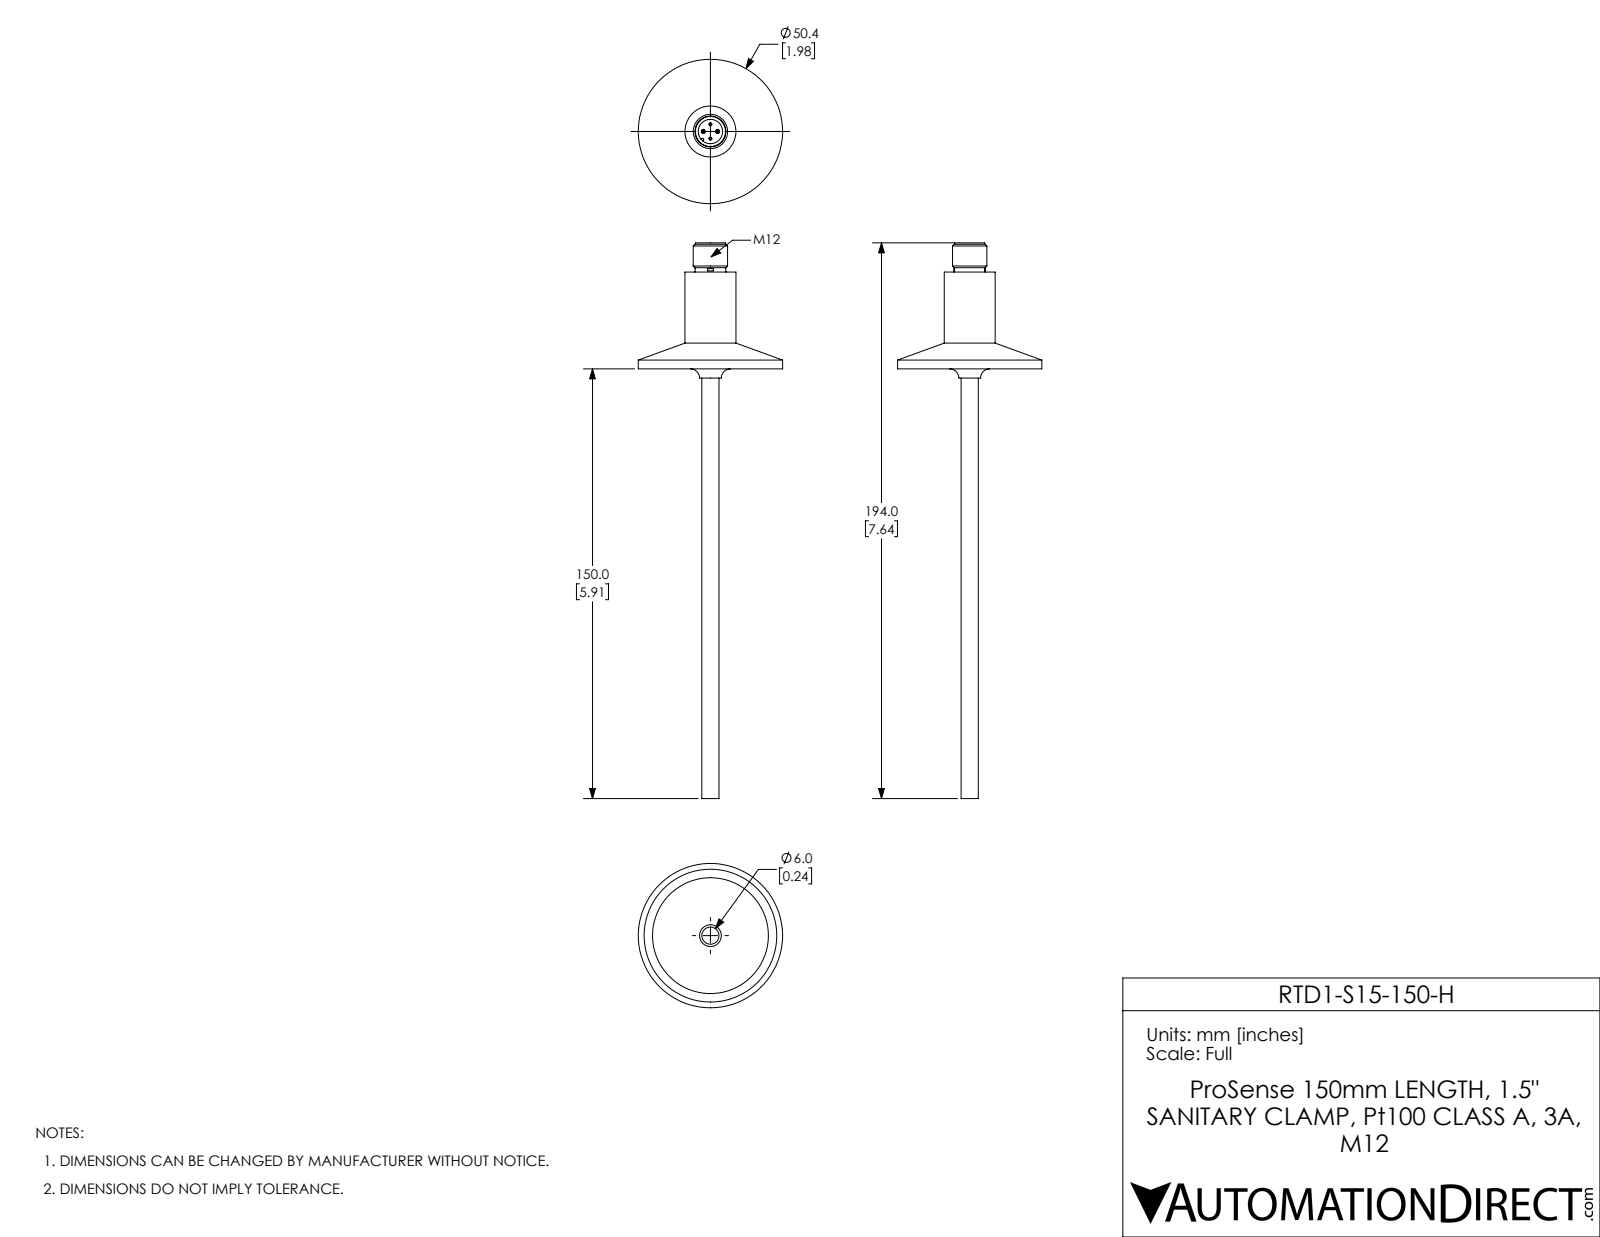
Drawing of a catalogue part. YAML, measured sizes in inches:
part_name: "RTD1-S15-150-H"
step_written_by: "SolidWorks 2017 (AUTOMOTIVE_DESIGN)"
units: inches
bodies: {solids: 1, faces: 79, planar: 26, cylindrical: 23, other: 30}
overall_size: [7.638, 1.984, 1.984]
volume: 1.38
surface_area: 15.06
round_holes:
  - {diameter: 0.335, count: 1}
round_bosses_or_shafts:
  - {diameter: 0.04, count: 4}
  - {diameter: 1.984, count: 1}
  - {diameter: 0.701, count: 1}
  - {diameter: 0.472, count: 1}
  - {diameter: 0.421, count: 1}
  - {diameter: 0.413, count: 1}
  - {diameter: 0.236, count: 1}
partial_cylinders:
  - {radius: 0.016, count: 1}
face_to_face_distances: [1.331, 1.378, 0.047, 1.732, 0.402, 0.354, 5.906, 7.236, 7.283, 7.638]
